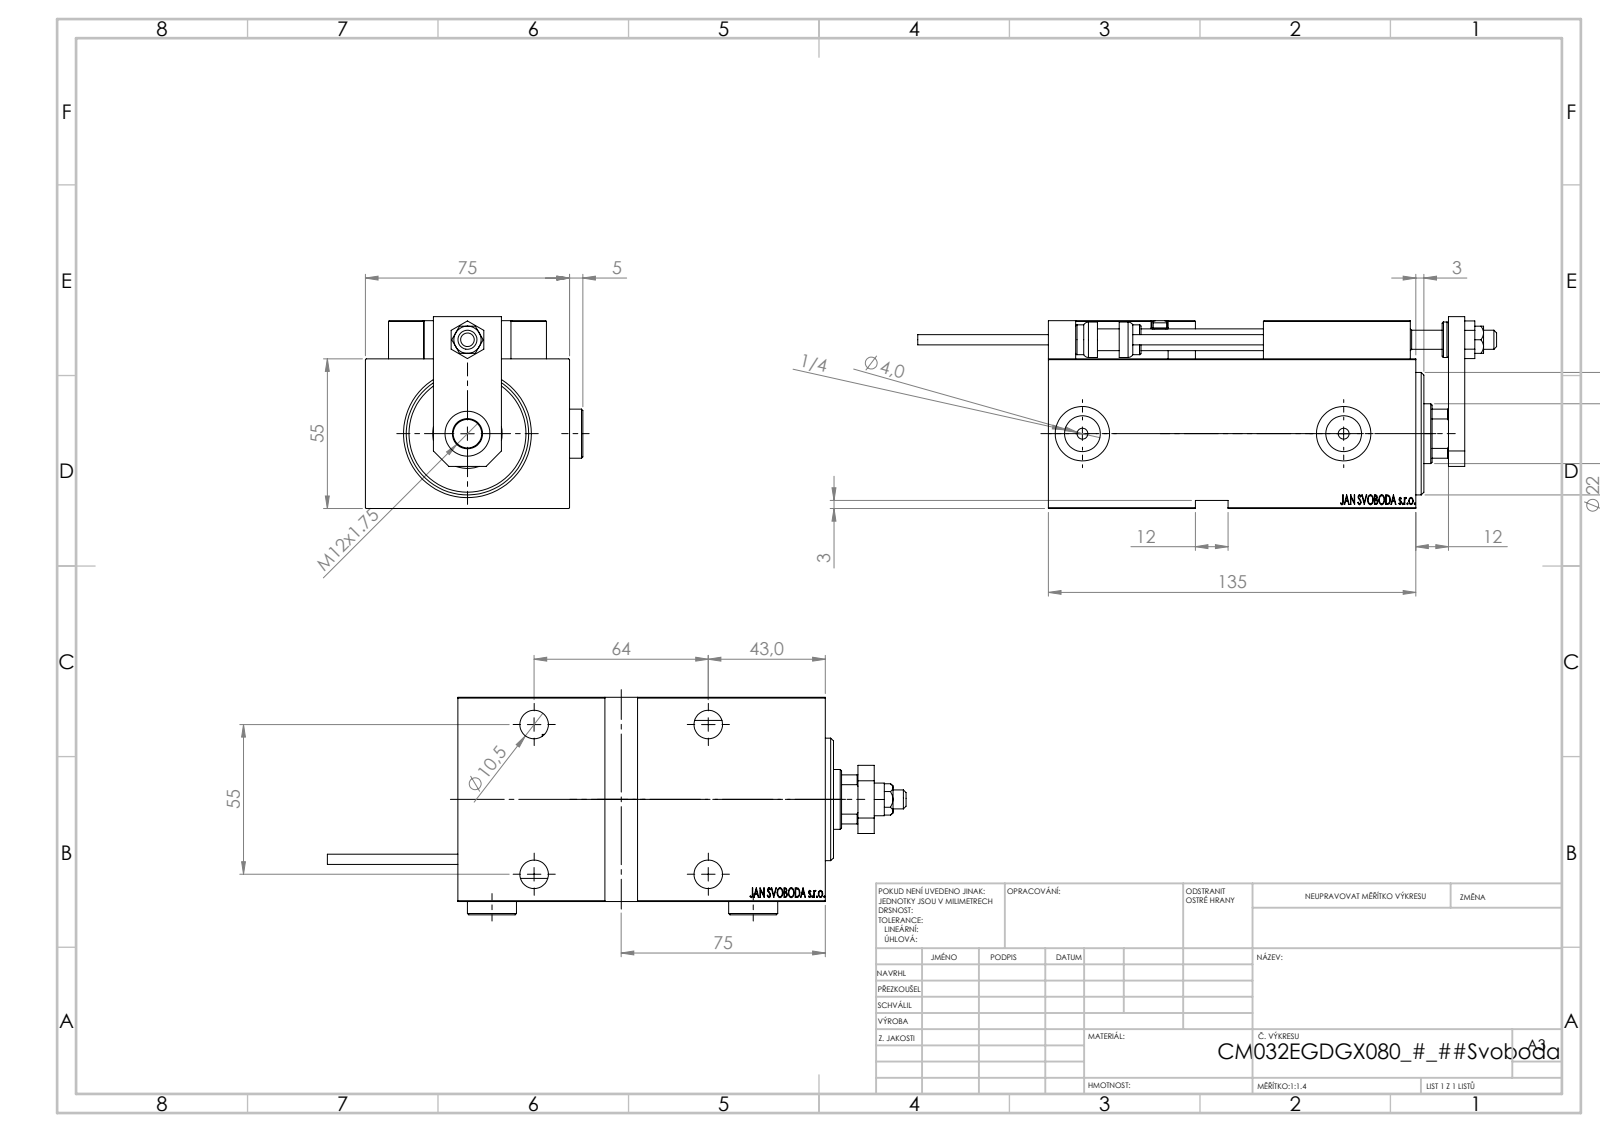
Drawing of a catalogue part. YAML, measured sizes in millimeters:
part_name: "KONCOVKA; V450CM_E_Body; V450CM_E_VCP; SWITCH X (+8 more)"
step_written_by: "SolidWorks 2019 (CONFIG_CONTROL_DESIGN)"
units: millimeters
bodies: {solids: 26, faces: 1346, planar: 605, cylindrical: 196, other: 545}
overall_size: [212.7, 79.9, 70.5]
volume: 547387
surface_area: 113054
round_holes:
  - {diameter: 4, count: 6}
  - {diameter: 8, count: 5}
  - {diameter: 10.5, count: 5}
  - {diameter: 16.5, count: 5}
  - {diameter: 3.2, count: 4}
  - {diameter: 5, count: 2}
  - {diameter: 13.16, count: 2}
  - {diameter: 20, count: 2}
  - {diameter: 7, count: 1}
  - {diameter: 22, count: 1}
  - {diameter: 25.5, count: 1}
  - {diameter: 32, count: 1}
round_bosses_or_shafts:
  - {diameter: 18, count: 2}
  - {diameter: 5, count: 2}
  - {diameter: 3.8, count: 2}
  - {diameter: 34, count: 1}
  - {diameter: 13, count: 1}
  - {diameter: 11, count: 1}
partial_cylinders:
  - {radius: 0.3, count: 30}
  - {radius: 3, count: 2}
  - {radius: 10.5, count: 1}
face_to_face_distances: [55, 75, 10, 69, 3, 14, 12, 135, 5, 25]
hole_center_spacings: [11.37, 20, 28.9, 29.59, 29.69, 36.06, 40.03, 42.19]
